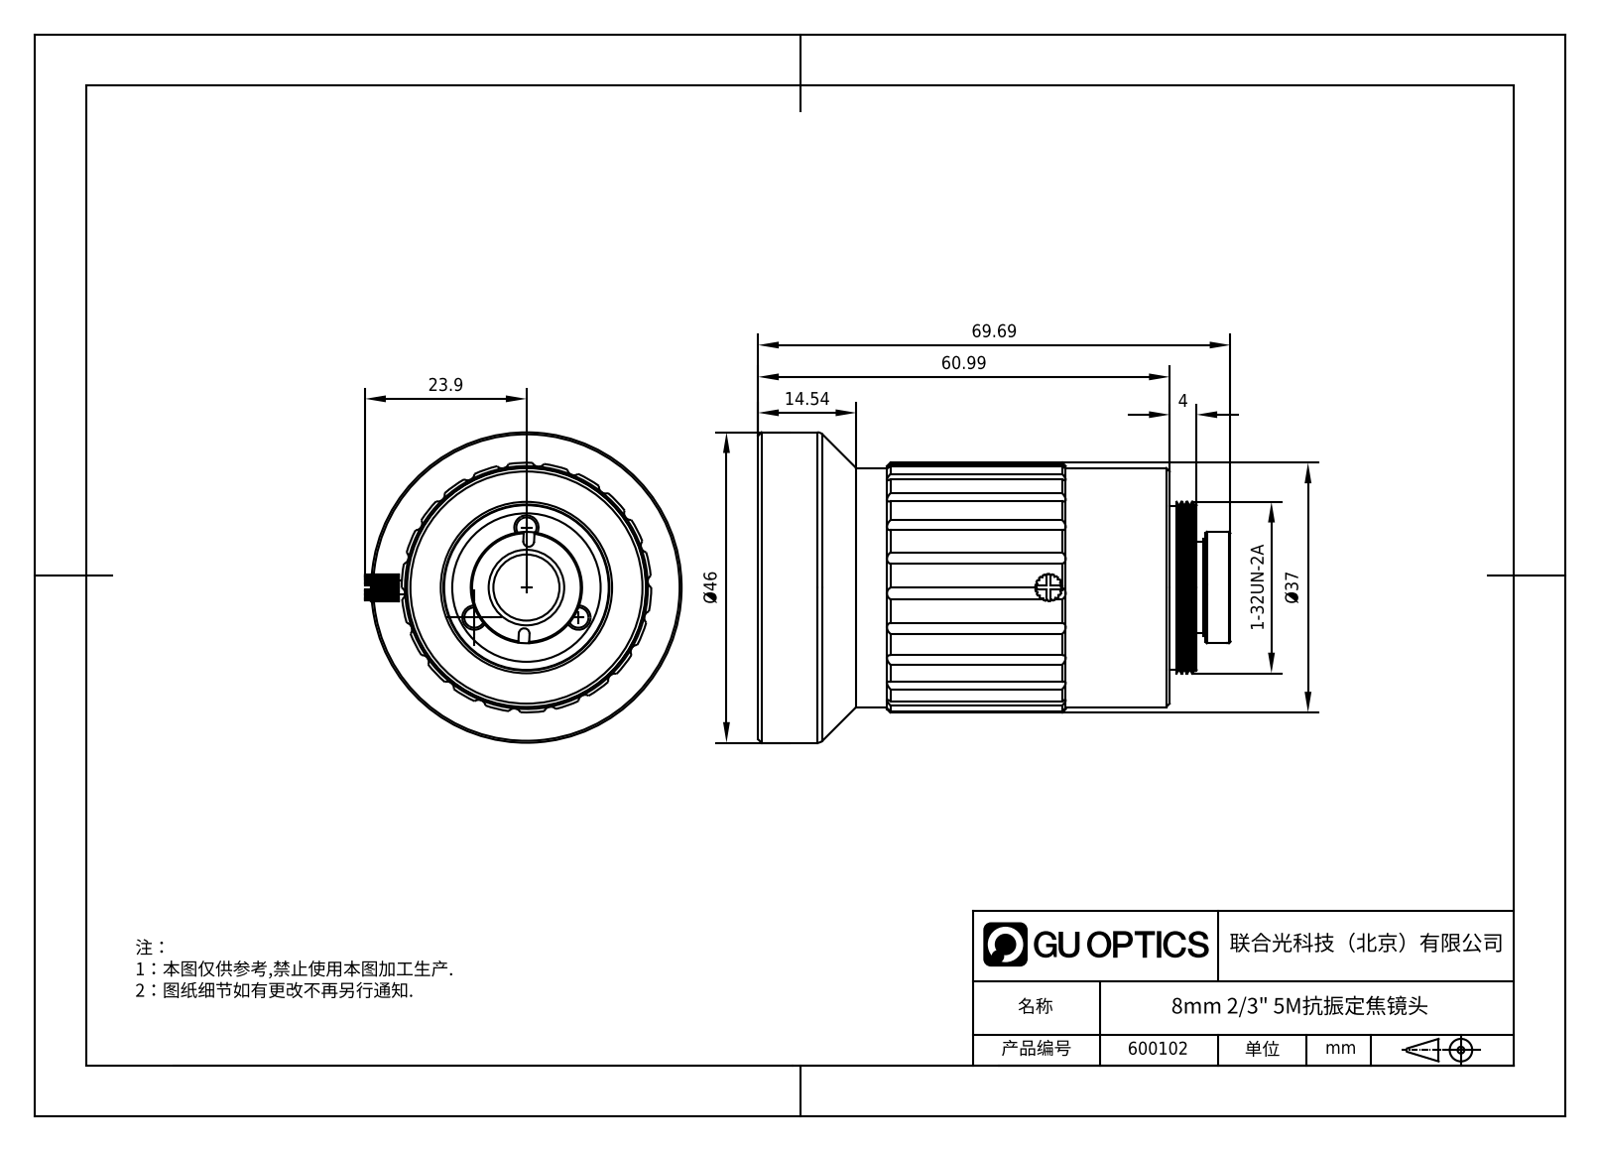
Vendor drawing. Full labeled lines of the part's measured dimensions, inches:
Part name (STEP PRODUCT): 600102
STEP written by: SolidWorks 2020 (CONFIG_CONTROL_DESIGN)
Units: inches
Bodies: 14 solids, 470 faces (188 planar, 189 cylindrical, 93 other)
Overall size (bounding box): 2.756 × 1.846 × 1.811
Volume: 2.471 in³ · Surface area: 55.29 in²
Round holes (diameter × count): ⌀0.067 ×6, ⌀0.055 ×3, ⌀0.087 ×3, ⌀0.118 ×3, ⌀0.213 ×1, ⌀0.248 ×1, ⌀0.268 ×1, ⌀0.287 ×1, ⌀0.307 ×1, ⌀0.327 ×1, ⌀0.346 ×1, ⌀0.366 ×1
Round bosses / shafts (diameter × count): ⌀0.079 ×4, ⌀0.142 ×3, ⌀1.811 ×1, ⌀1.457 ×1, ⌀1.417 ×1, ⌀1.394 ×1, ⌀1.26 ×1, ⌀1.181 ×1
Partial cylindrical surfaces — rounded edges, fillets, slot ends (radius × count): R0.039 ×22, R0.049 ×6, R0.031 ×2, R0.197 ×2, R0.079 ×1
Main face-to-face distances: 2.283, 1.222, 2.151, 0.132, 1.657, 0.494, 0.626, 0.276, 0.197, 0.13
Hole centre spacings: 0.35, 0.381, 0.607
